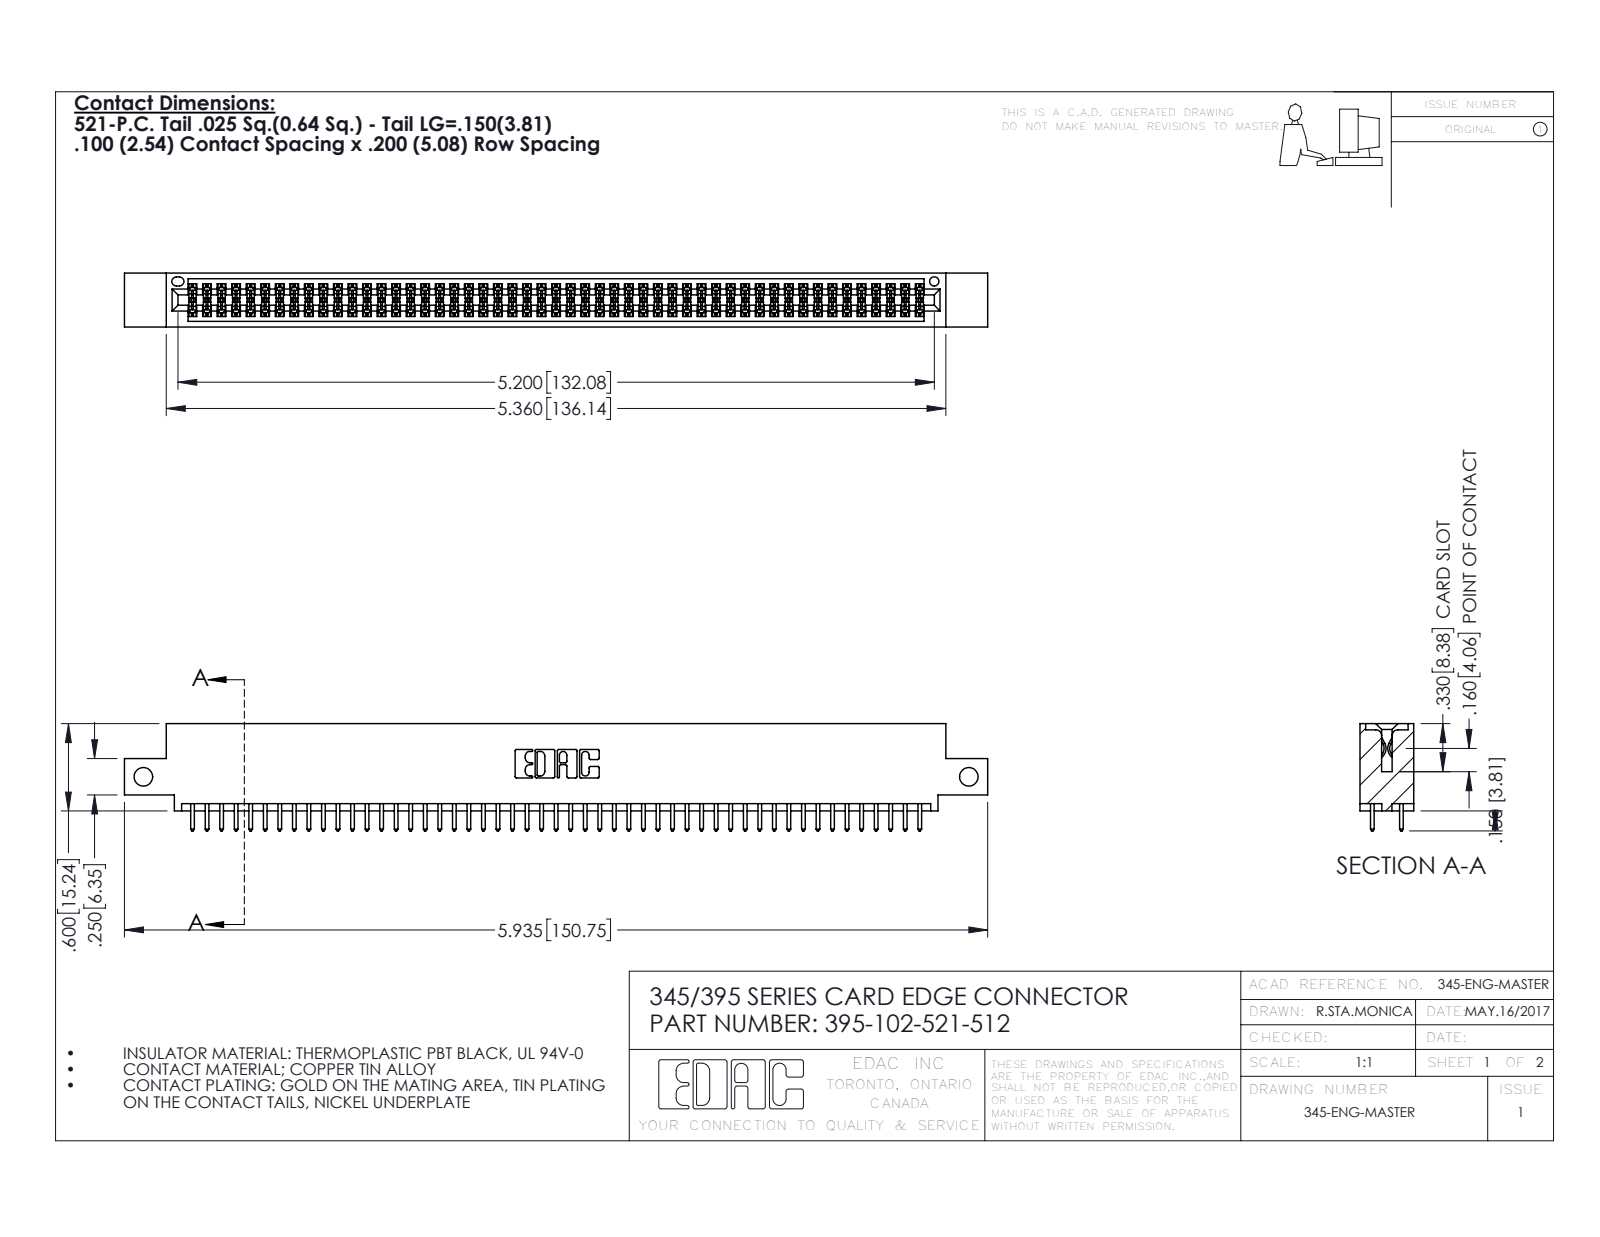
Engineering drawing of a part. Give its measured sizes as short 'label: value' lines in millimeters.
name: 395-102-521-512; 345-292-001_345-293-121; 345 Part_0.110 Offset - Side Mount
written by: SolidWorks 2016 (CONFIG_CONTROL_DESIGN)
unit: mm
bodies: 103 solids, 5230 faces (3450 planar, 1780 cylindrical, 0 other)
size: 150.7 × 18.7 × 9.4
volume: 14 500 mm³; area: 21 330 mm²
holes: 2× ⌀3.3, 1× ⌀1.6
rounds: 153× R0.2, 102× R0.3, 22× R0.3, 6× R0.2, 6× R0.8, 3× R0.7, 2× R0.4, 2× R0.5
face distances: 7.6, 1.8, 5.1, 2.5, 6.9, 0.6, 9.4, 5.7, 4.4, 3.8
hole spacings: 144.1
